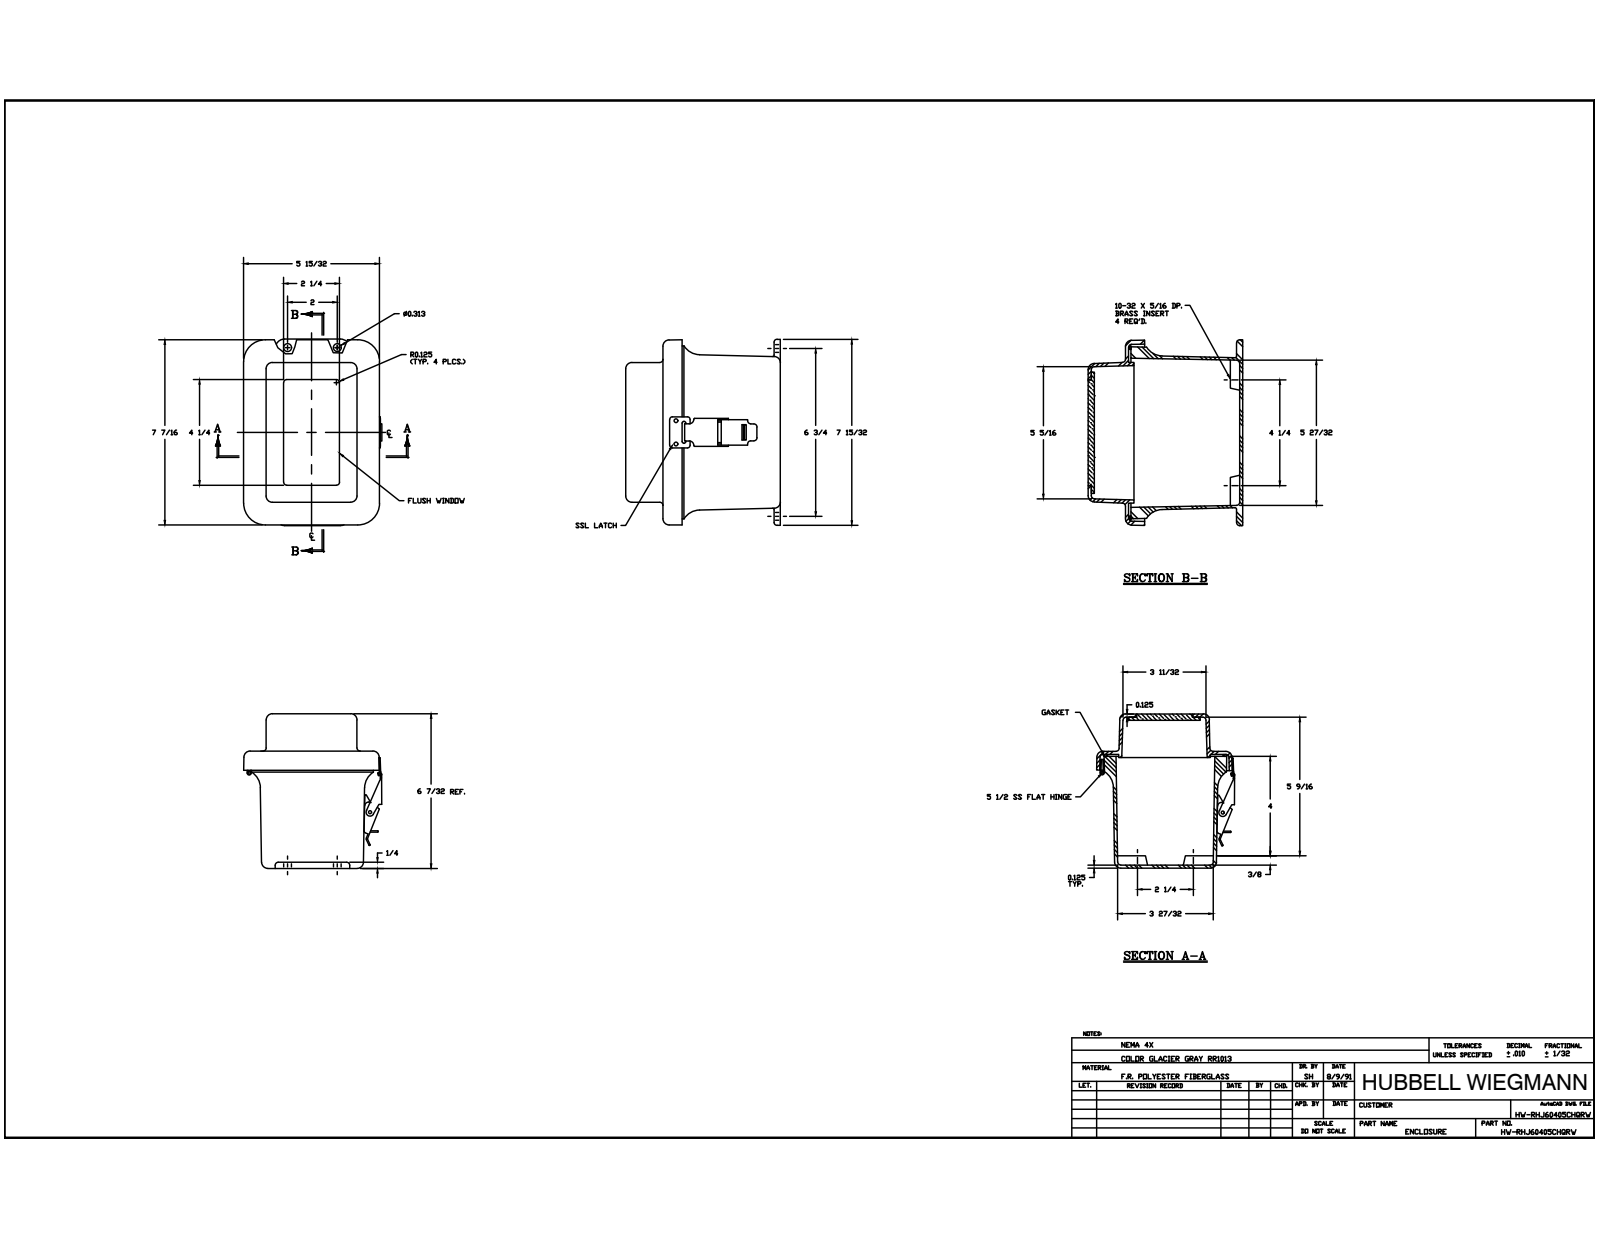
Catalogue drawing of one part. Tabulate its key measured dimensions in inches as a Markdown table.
| quantity | value |
| --- | --- |
| part name | J604HL_8; RMINS45821P_85; RMINS45821P_86; RMINS45821P_87 (+8 more) |
| STEP written by | Autodesk Inventor 2014 (AUTOMOTIVE_DESIGN) |
| units | inches |
| bodies | 26 solids, 721 faces (287 planar, 286 cylindrical, 148 other) |
| overall size | 7.474 × 6.227 × 5.601 |
| volume | 35.43 in³ |
| surface area | 474.9 in² |
| round holes (diameter × count) | 0.14 × 11, 0.131 × 5, 0.152 × 5, 0.104 × 4, 0.156 × 4, 0.218 × 4, 0.13 × 2, 0.135 × 2, 0.085 × 1, 0.375 × 1 |
| round bosses / shafts (diameter × count) | 0.125 × 9, 0.25 × 5, 0.27 × 4, 0.3 × 1, 0.17 × 1, 0.155 × 1, 0.12 × 1 |
| partial cylindrical surfaces (radius × count) | 0.125 × 28, 0.031 × 20, 0.25 × 16, 0.015 × 12, 0.045 × 8, 0.03 × 6, 0.022 × 5, 0.06 × 4 |
| main face-to-face distances | 0.125, 4.602, 6.102, 1.5, 0.25, 0.125, 5.977, 5.852, 6.227, 1.625 |
| hole center spacings | 0.937, 2.5, 3.339, 0.75, 0.469, 0.5, 1.341, 1.467 |
